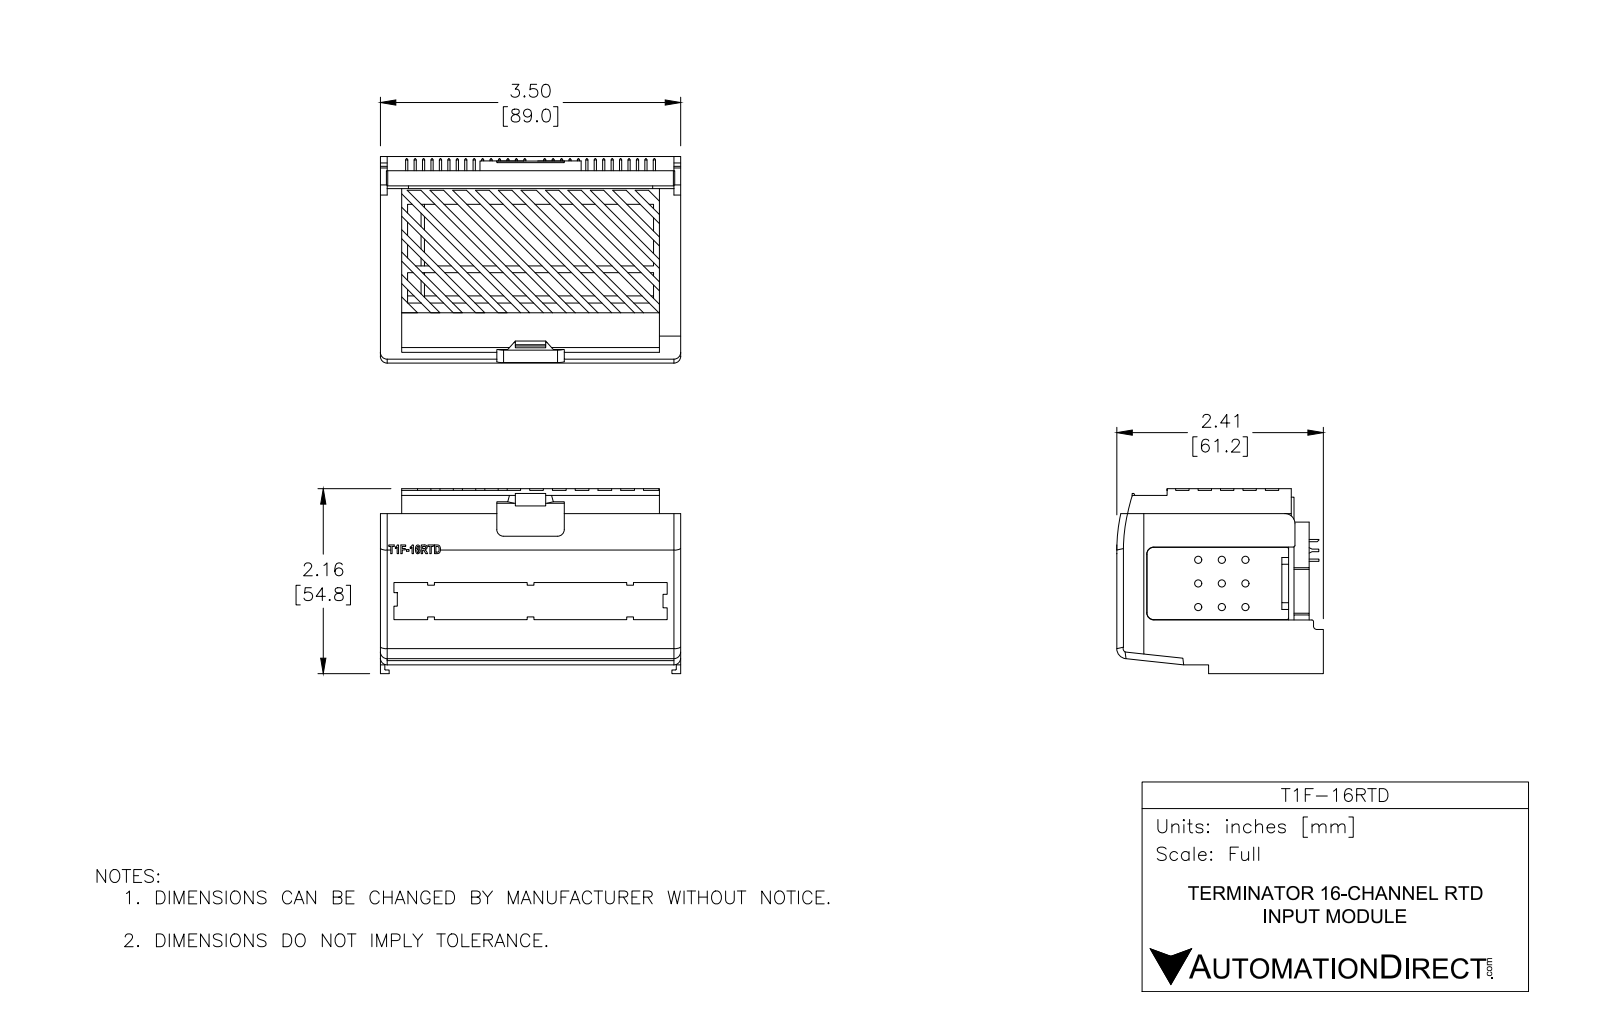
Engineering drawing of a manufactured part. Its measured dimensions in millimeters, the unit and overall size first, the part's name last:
Units: millimetres
Overall size (bounding box): 88.7 × 65.1 × 61.36
Round holes (diameter × count): ⌀3 ×16
Round bosses / shafts (diameter × count): ⌀0.7 ×56
Partial cylindrical surfaces — rounded edges, fillets, slot ends (radius × count): R3.5 ×18, R1 ×5, R0.25 ×3, R0.55 ×3, R1.5 ×2, R8 ×1, R10 ×1, R18 ×1
Main face-to-face distances: 2, 86.7, 55.35, 0.5, 59.8, 88.7, 1.5, 55.26, 53.35, 84.7
Hole centre spacings: 5.15, 10.3, 15.45, 20.6, 25.75, 30.9, 36.05, 41.2
Volume: 45 450 mm³ · Surface area: 54 522 mm²
Bodies: 1 solid, 646 faces (446 planar, 181 cylindrical, 19 other)
Part name (STEP PRODUCT): T1F-16RTD
STEP written by: SolidWorks 2013 (AUTOMOTIVE_DESIGN)
